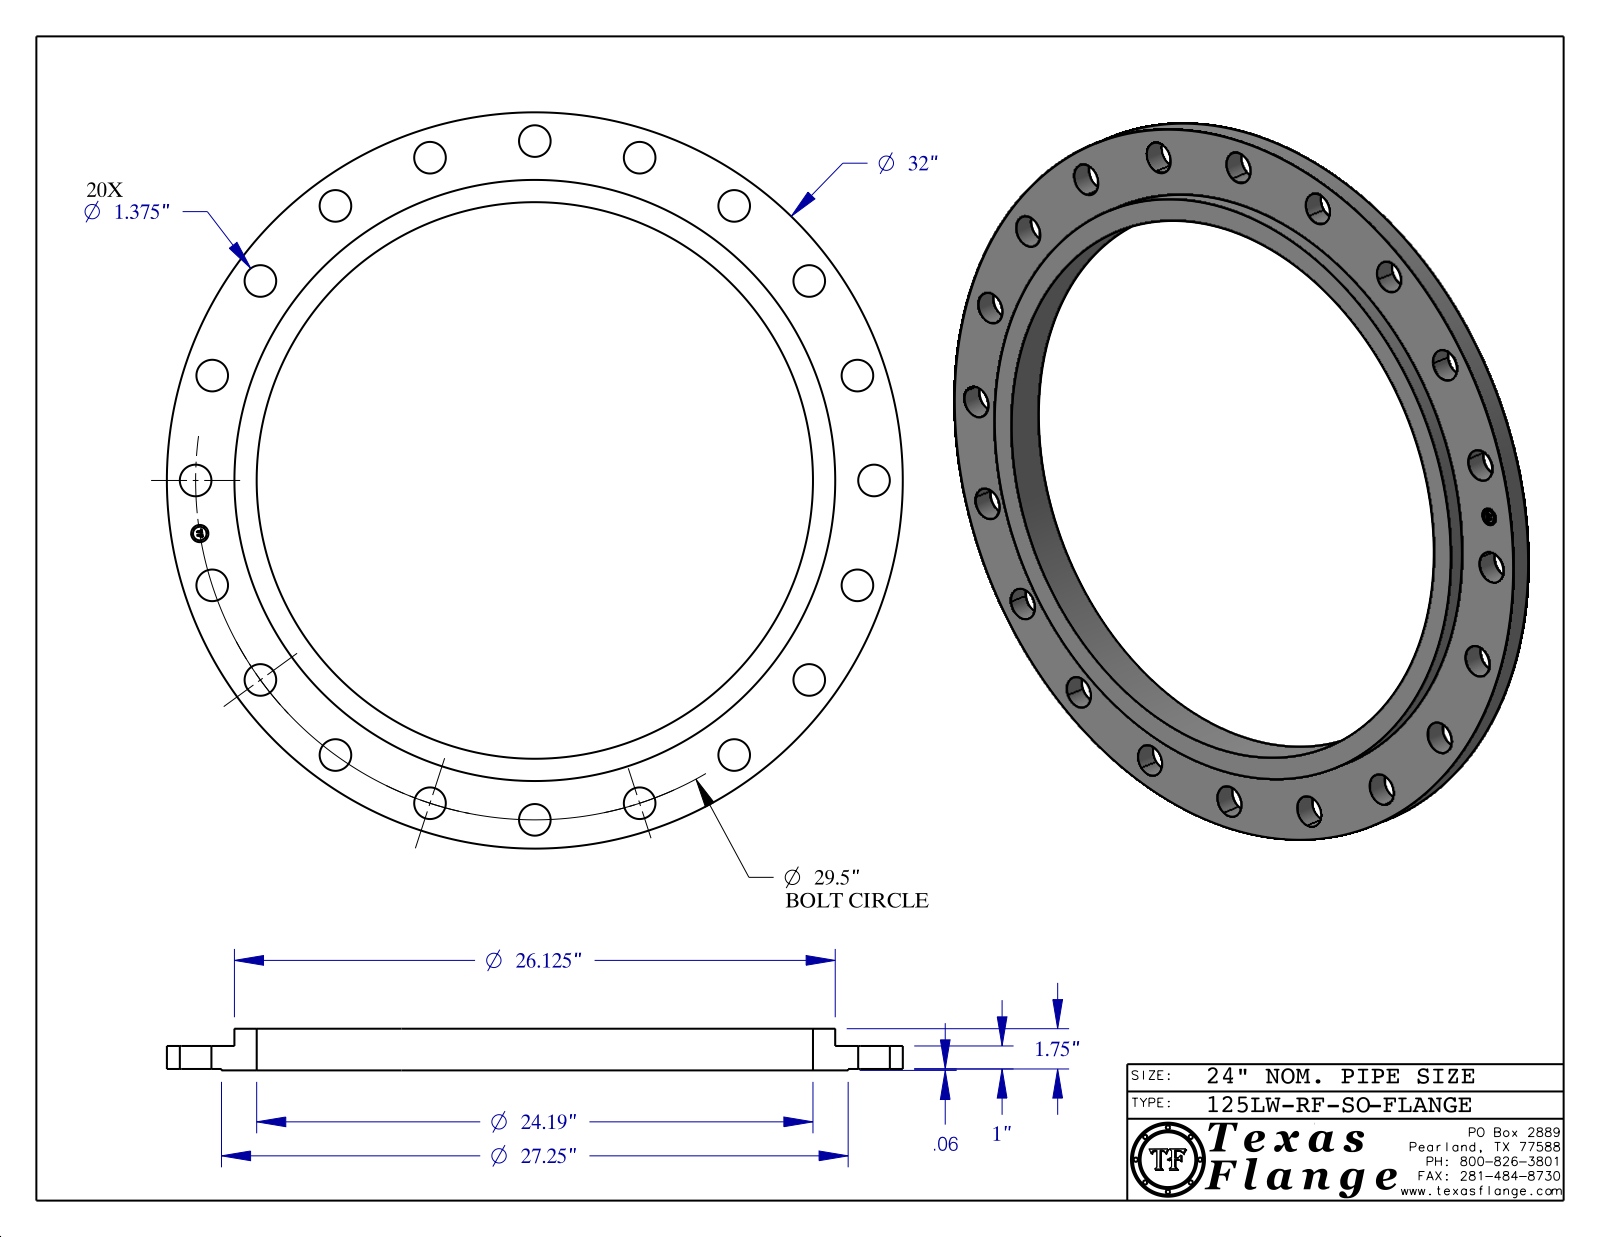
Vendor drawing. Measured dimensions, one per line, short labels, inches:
name: 125LW-RF-SO-B16.1
written by: CATIA V5 STEP AP214 (AUTOMOTIVE_DESIGN)
unit: in
bodies: 1 solid, 437 faces (369 planar, 68 cylindrical, 0 other)
size: 32 × 32 × 1.813
volume: 380 in³; area: 1 022 in²
holes: 20× ⌀1.375, 1× ⌀0.75, 1× ⌀24.19
bosses: 8× ⌀0.045, 1× ⌀32, 1× ⌀27.25, 1× ⌀26.125, 1× ⌀0.591
face distances: 1, 0.063, 1.063, 1.813, 1.75, 0.75, 1.048, 0.985, 0.015, 0.765
hole spacings: 14.75, 29.137, 4.615, 17.34, 20.859, 23.866, 26.285, 9.116
